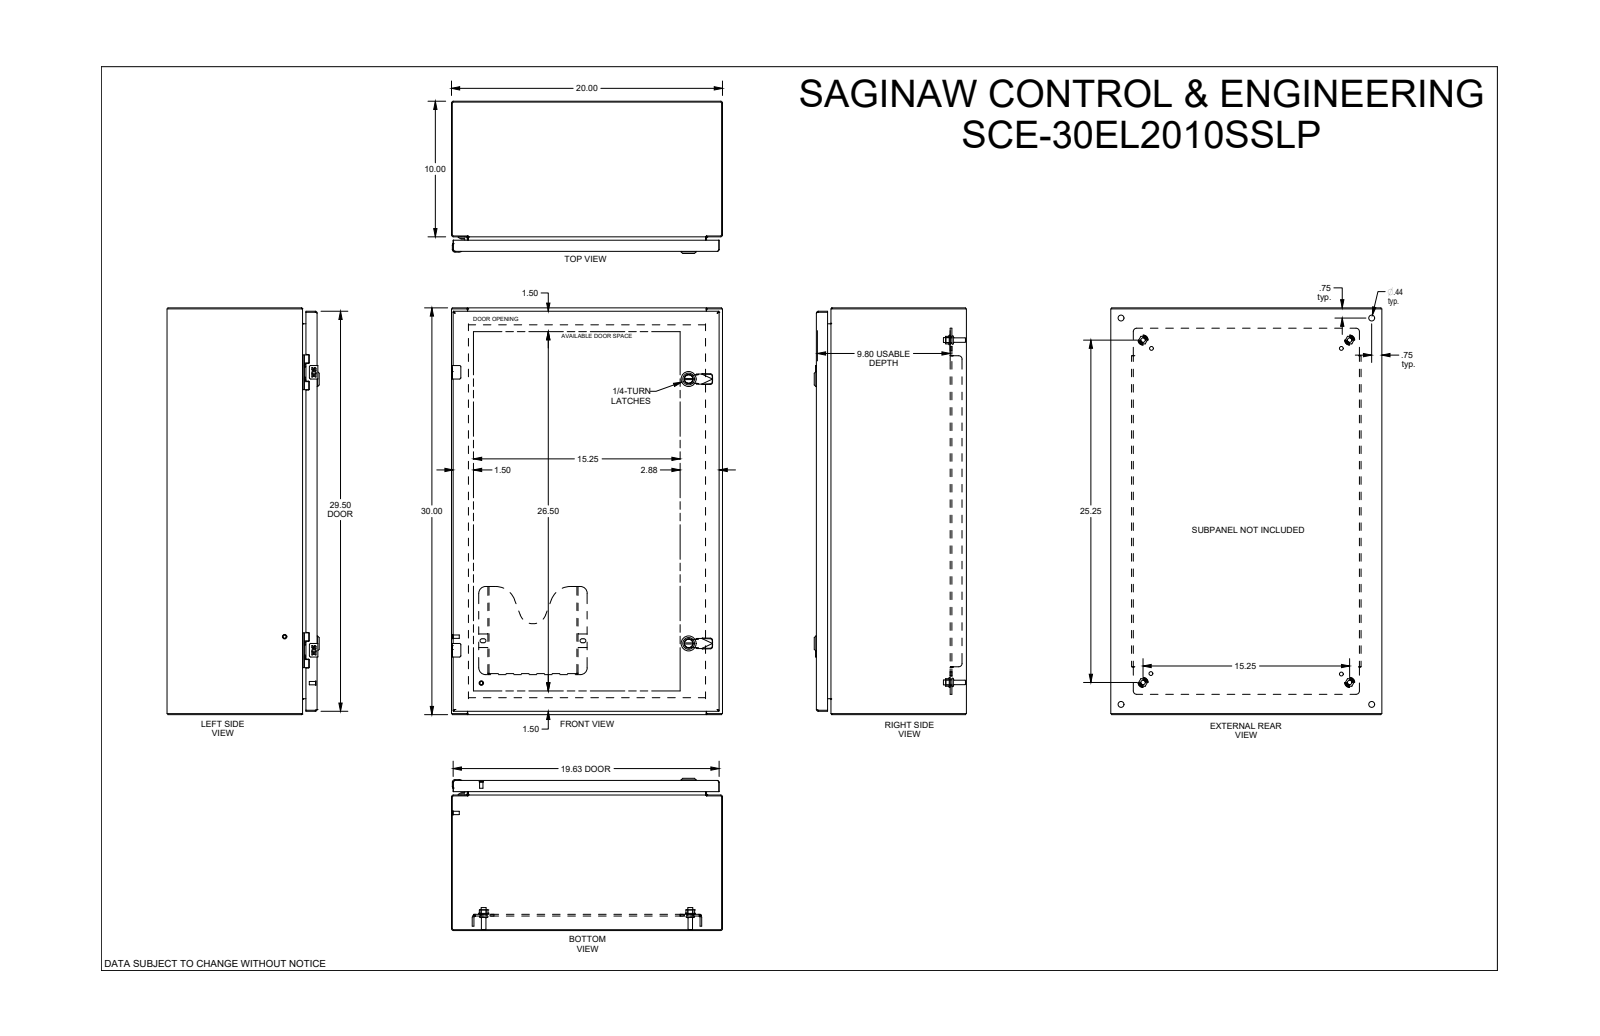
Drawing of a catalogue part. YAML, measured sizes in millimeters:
part_name: "SCE-30EL2010SSLP"
step_written_by: "SolidWorks 2019 (CONFIG_CONTROL_DESIGN)"
units: millimeters
bodies: {solids: 0, faces: 2806, planar: 1297, cylindrical: 749, other: 760}
overall_size: [762, 508, 285.2]
round_holes:
  - {diameter: 4.4, count: 4}
  - {diameter: 5.2, count: 4}
  - {diameter: 6.2, count: 4}
  - {diameter: 6.8, count: 4}
  - {diameter: 7.1, count: 4}
  - {diameter: 9.3, count: 4}
  - {diameter: 11.1, count: 4}
  - {diameter: 12.7, count: 4}
  - {diameter: 9.5, count: 3}
  - {diameter: 4, count: 2}
  - {diameter: 5, count: 2}
  - {diameter: 5.5, count: 2}
round_bosses_or_shafts:
  - {diameter: 4.3, count: 6}
  - {diameter: 9.3, count: 4}
  - {diameter: 8.4, count: 4}
  - {diameter: 6.4, count: 4}
  - {diameter: 6.3, count: 4}
  - {diameter: 5, count: 3}
  - {diameter: 28, count: 2}
  - {diameter: 22, count: 2}
partial_cylinders:
  - {radius: 0.3, count: 56}
  - {radius: 0.4, count: 32}
  - {radius: 0.3, count: 28}
  - {radius: 1, count: 23}
  - {radius: 0.5, count: 20}
  - {radius: 0.7, count: 12}
  - {radius: 1.8, count: 10}
  - {radius: 3.7, count: 10}
face_to_face_distances: [1.9, 1.9, 277.4, 279.3, 506.1, 281.3, 279.3, 3.2, 25.4, 252]
hole_center_spacings: [520.7, 25, 0.5, 22.2, 114.1, 430.6, 80.6, 372]
